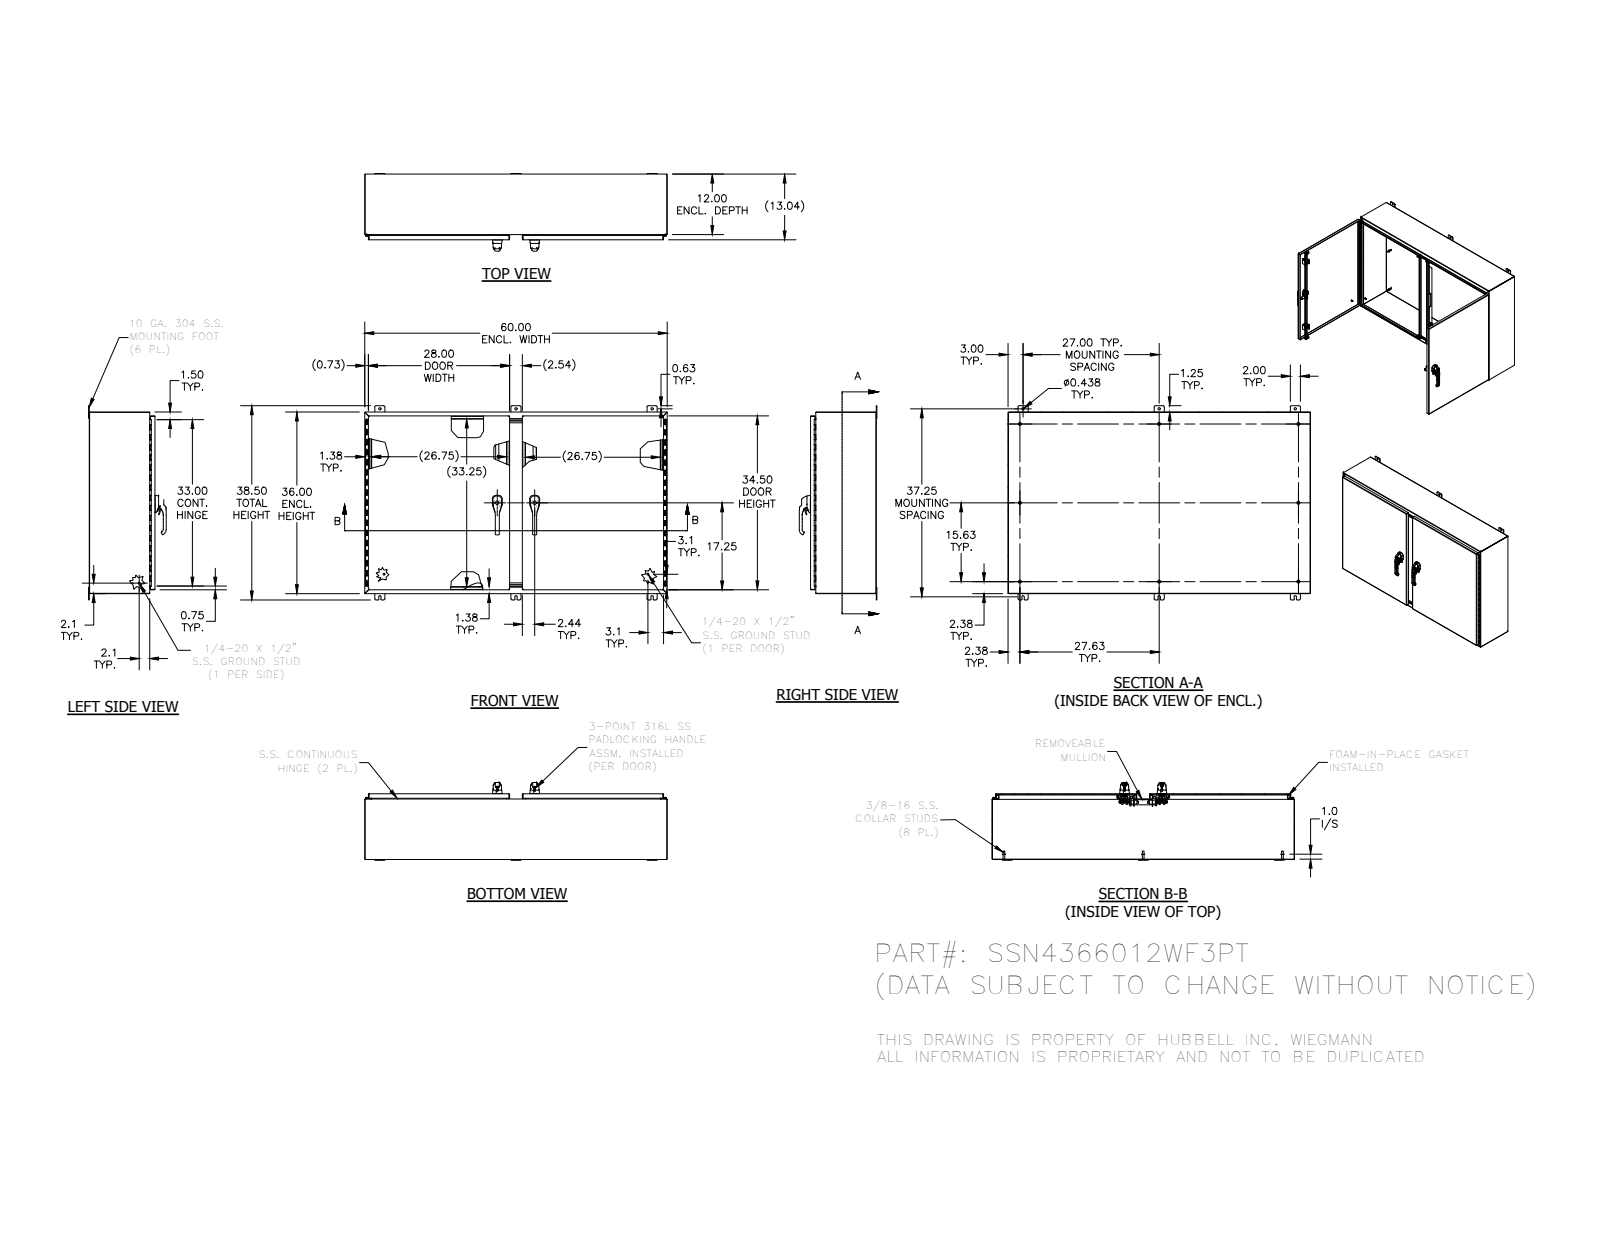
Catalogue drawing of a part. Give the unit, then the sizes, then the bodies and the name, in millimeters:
Units: millimetres
Overall size (bounding box): 1524 × 977.9 × 391.4
Round holes (diameter × count): ⌀6.7 ×12, ⌀4.7 ×8, ⌀5.4 ×6, ⌀7.1 ×6, ⌀11.1 ×6, ⌀5 ×4, ⌀6.4 ×4, ⌀7.1 ×4, ⌀8 ×4, ⌀10.2 ×4, ⌀10.2 ×4, ⌀11.4 ×4
Round bosses / shafts (diameter × count): ⌀6.4 ×9, ⌀15.9 ×8, ⌀8.4 ×8, ⌀13.5 ×6, ⌀6 ×5, ⌀13.5 ×4, ⌀11.1 ×4, ⌀11 ×4
Partial cylindrical surfaces — rounded edges, fillets, slot ends (radius × count): R0.5 ×317, R0.3 ×221, R0.5 ×39, R0.8 ×33, R3.2 ×31, R1.3 ×30, R6.4 ×30, R2 ×25
Main face-to-face distances: 1.9, 2.4, 328.7, 326.8, 331.1, 329.2, 912.5, 1522.1, 302.9, 910.6
Hole centre spacings: 9.7, 19.3, 188.4, 12.5, 12.5, 22.5, 31.4, 35
Volume: 10 460 000 mm³ · Surface area: 10 190 000 mm²
Bodies: 127 solids, 6644 faces (2382 planar, 2742 cylindrical, 1520 other)
Part name (STEP PRODUCT): 1091-74-03; HFW31712; HFW31234; HFW316325 (+8 more)
STEP written by: SolidWorks 2014 (AUTOMOTIVE_DESIGN)
